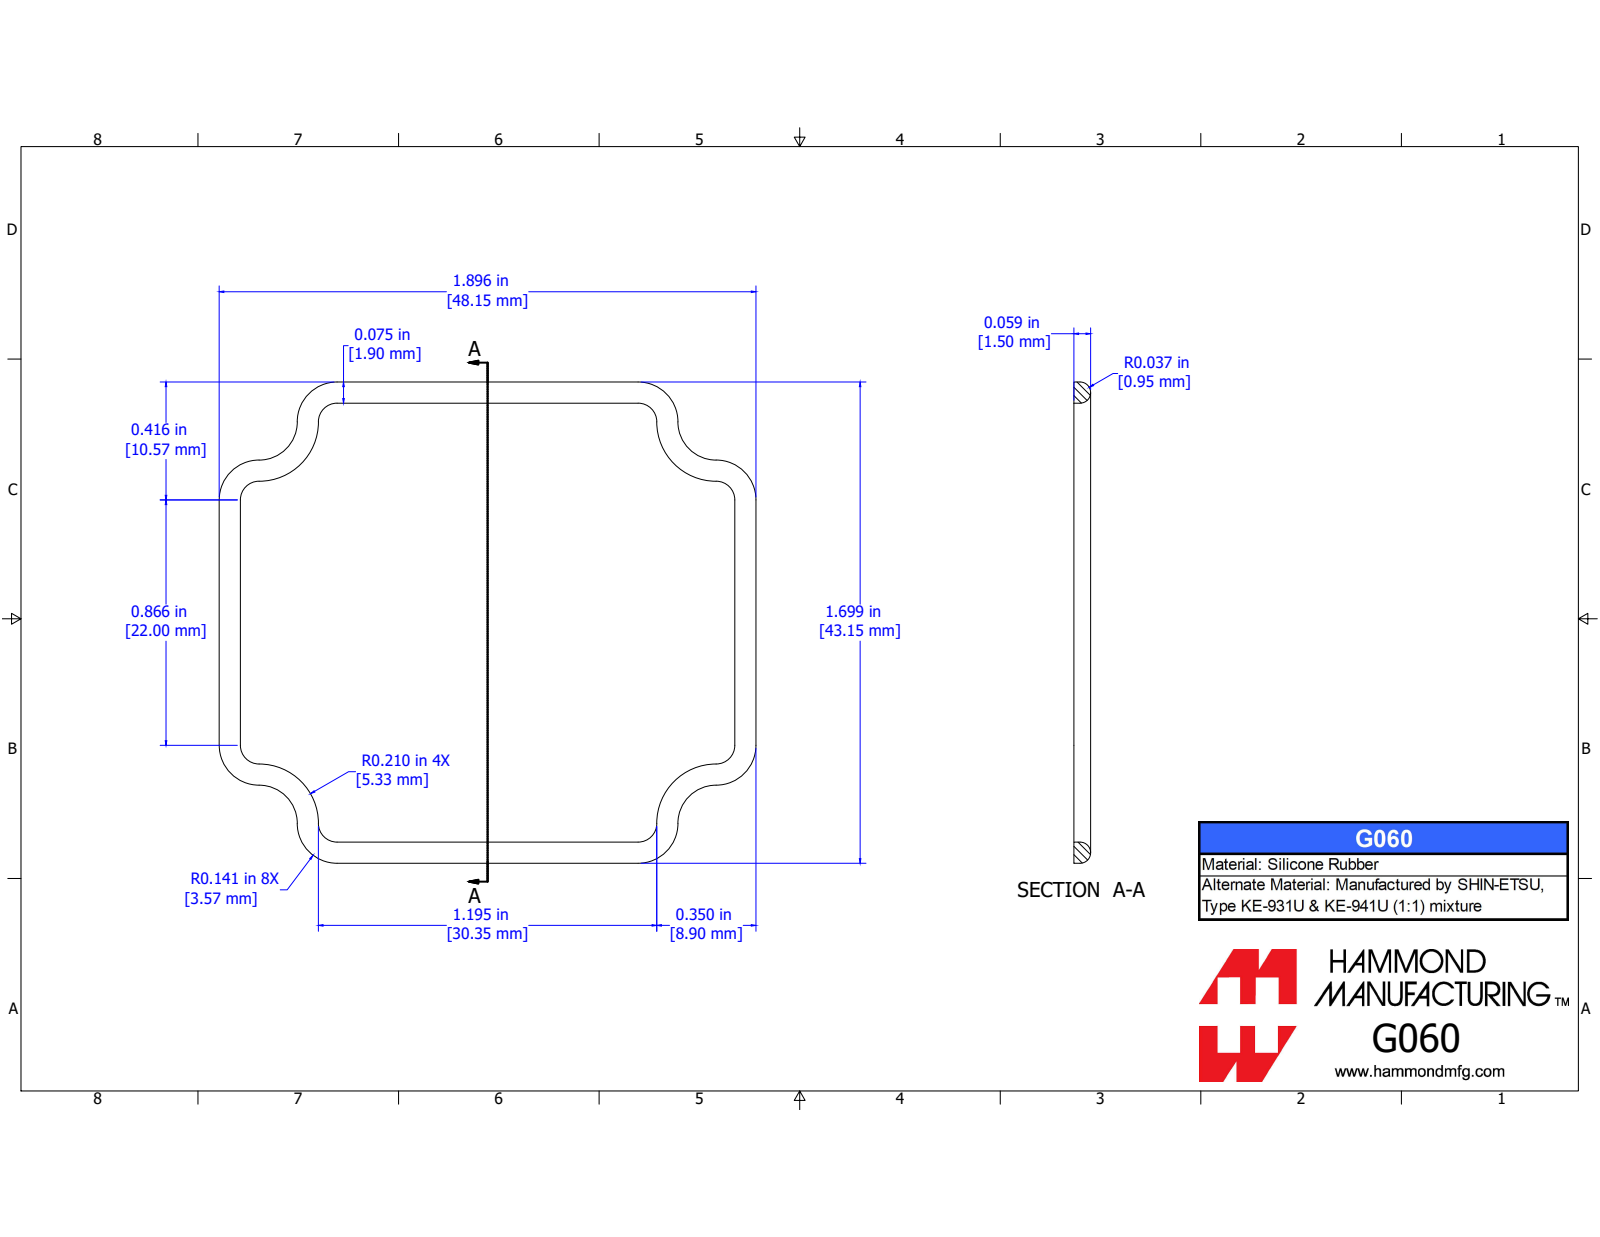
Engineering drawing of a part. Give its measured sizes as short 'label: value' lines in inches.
name: 1590Z060G
written by: SolidWorks 2019 (CONFIG_CONTROL_DESIGN)
unit: in
bodies: 1 solid, 147 faces (41 planar, 24 cylindrical, 82 other)
size: 1.898 × 1.701 × 0.093
volume: 0.042 in³; area: 1.959 in²
rounds: 16× R0.035
face distances: 1.607, 1.804, 0.091, 0.284, 1.519, 1.323, 1.235, 1.039, 0.093, 0.134
